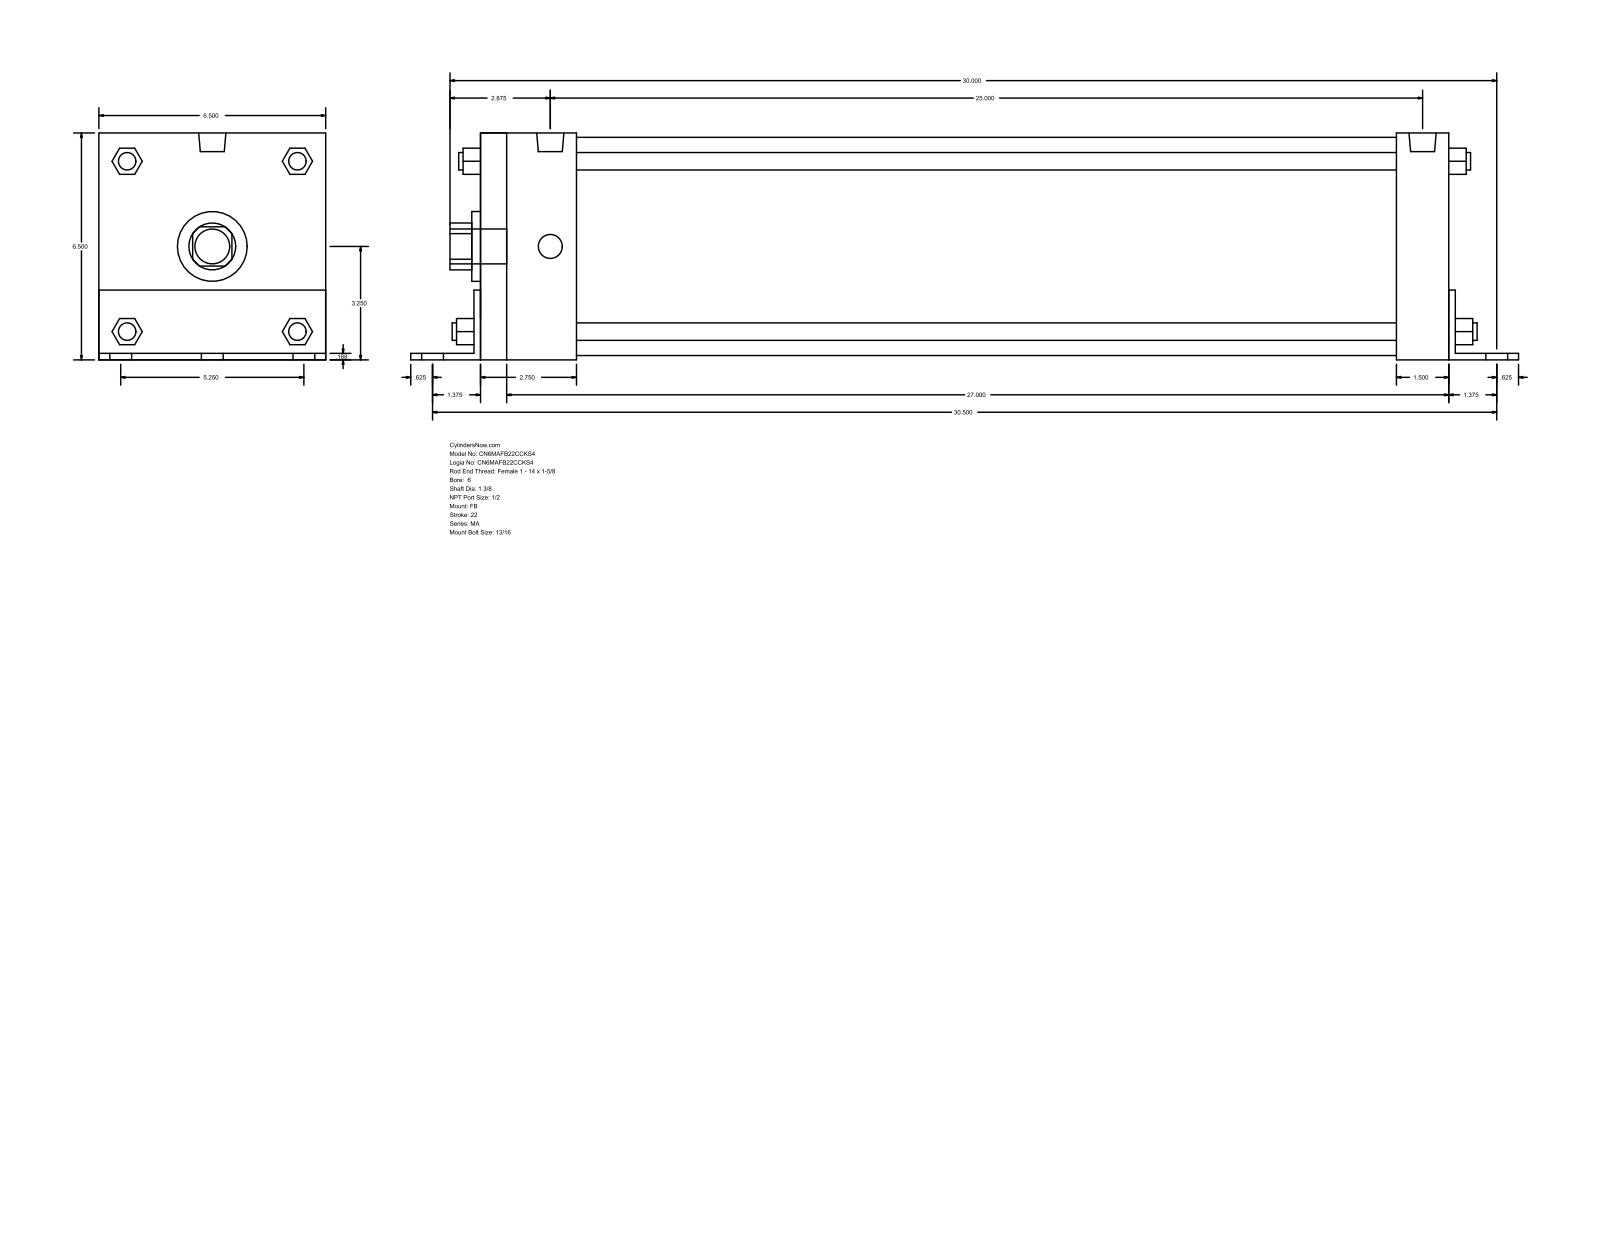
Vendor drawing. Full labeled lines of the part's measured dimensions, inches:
Part name (STEP PRODUCT): MA_FB__0600_1.375
STEP written by: GSSL Pune (CONFIG_CONTROL_DESIGN)
Units: inches
Bodies: 0 solids, 140 faces (105 planar, 35 cylindrical, 0 other)
Overall size (bounding box): 31.625 × 6.502 × 6.5
Round holes (diameter × count): ⌀1.375 ×1, ⌀2 ×1, ⌀6.25 ×1
Round bosses / shafts (diameter × count): ⌀0.813 ×6, ⌀0.687 ×4, ⌀0.5 ×4, ⌀0.778 ×2, ⌀1 ×1
Partial cylindrical surfaces — rounded edges, fillets, slot ends (radius × count): R0.672 ×1, R1.262 ×1
Main face-to-face distances: 6.5, 0.187, 27.625, 6.502, 0.185, 6.315, 0.188, 1.5, 27.813, 28
